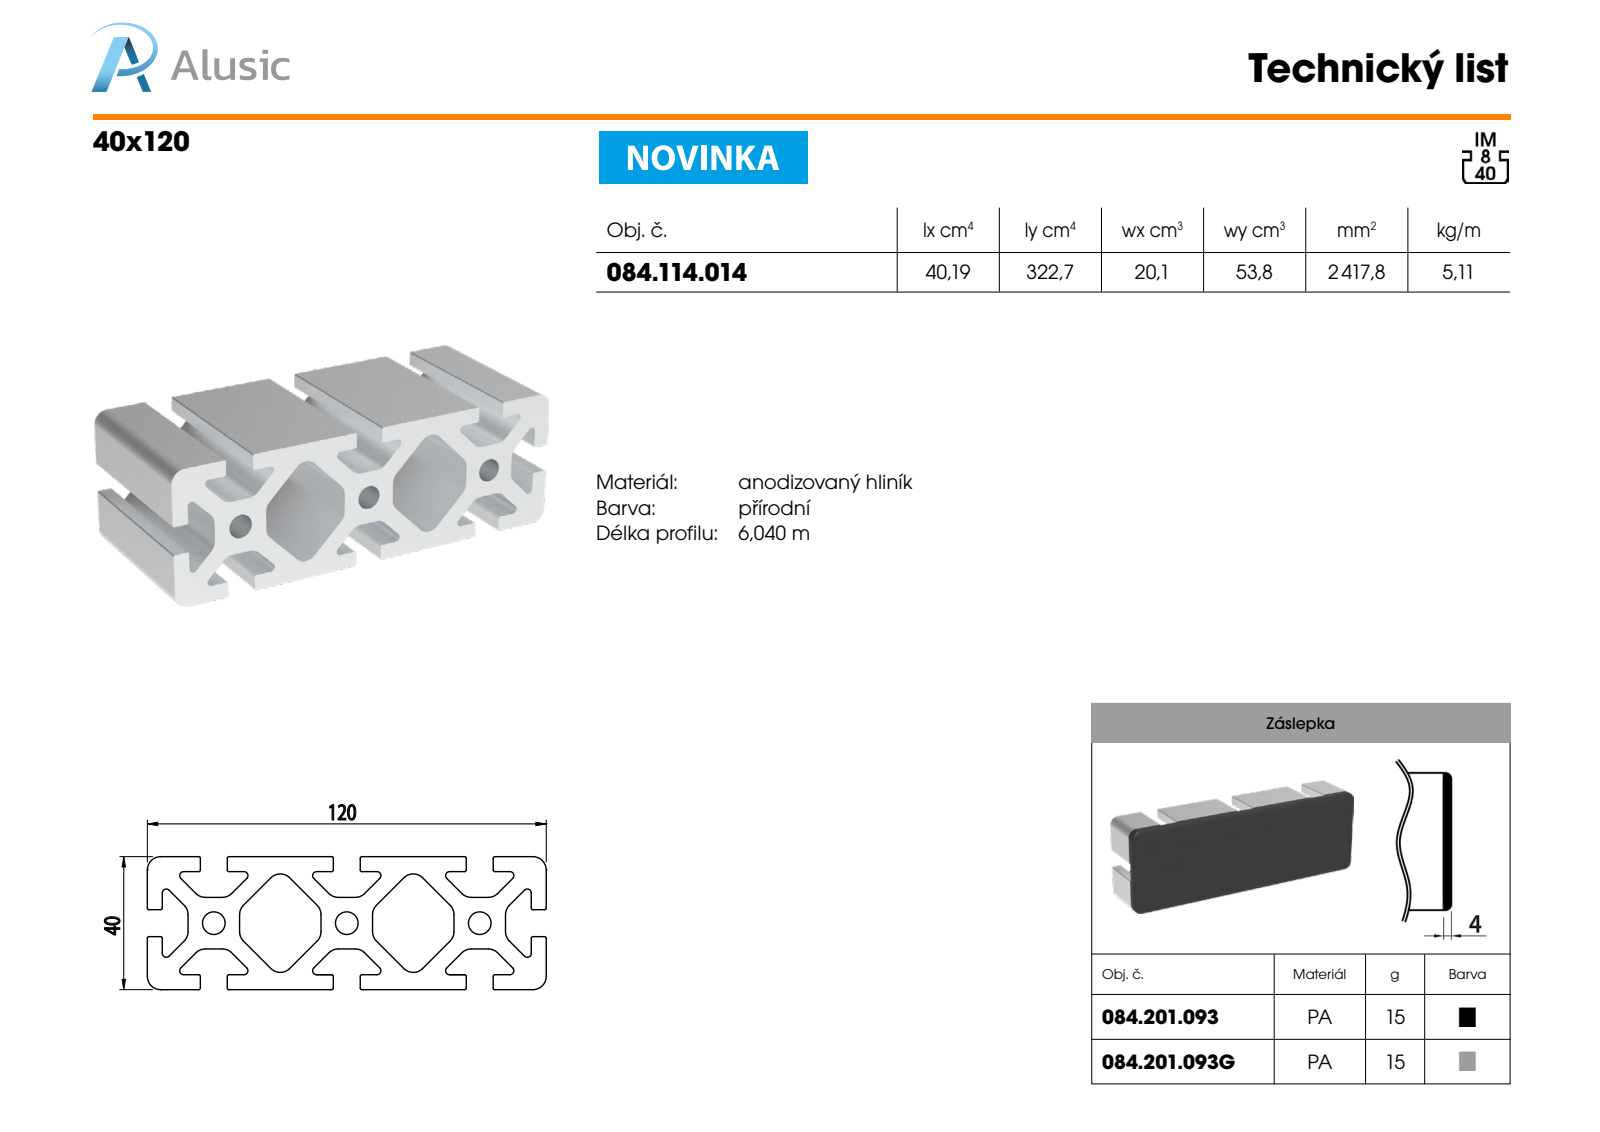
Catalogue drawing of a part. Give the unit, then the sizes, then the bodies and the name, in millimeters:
Units: millimetres
Overall size (bounding box): 119.9 × 39.9 × 10.6
Partial cylindrical surfaces — rounded edges, fillets, slot ends (radius × count): R0.3 ×10, R0.2 ×4, R2 ×4, R2.5 ×4, R4 ×4
Main face-to-face distances: 2.5, 1.5, 4, 39.9, 80, 119.9, 2.65, 1.35, 10.6, 8.1
Volume: 13 068 mm³ · Surface area: 11 493 mm²
Bodies: 1 solid, 366 faces (208 planar, 36 cylindrical, 122 other)
Part name (STEP PRODUCT): 084.201.093
STEP written by: SolidWorks 2018 (CONFIG_CONTROL_DESIGN)
